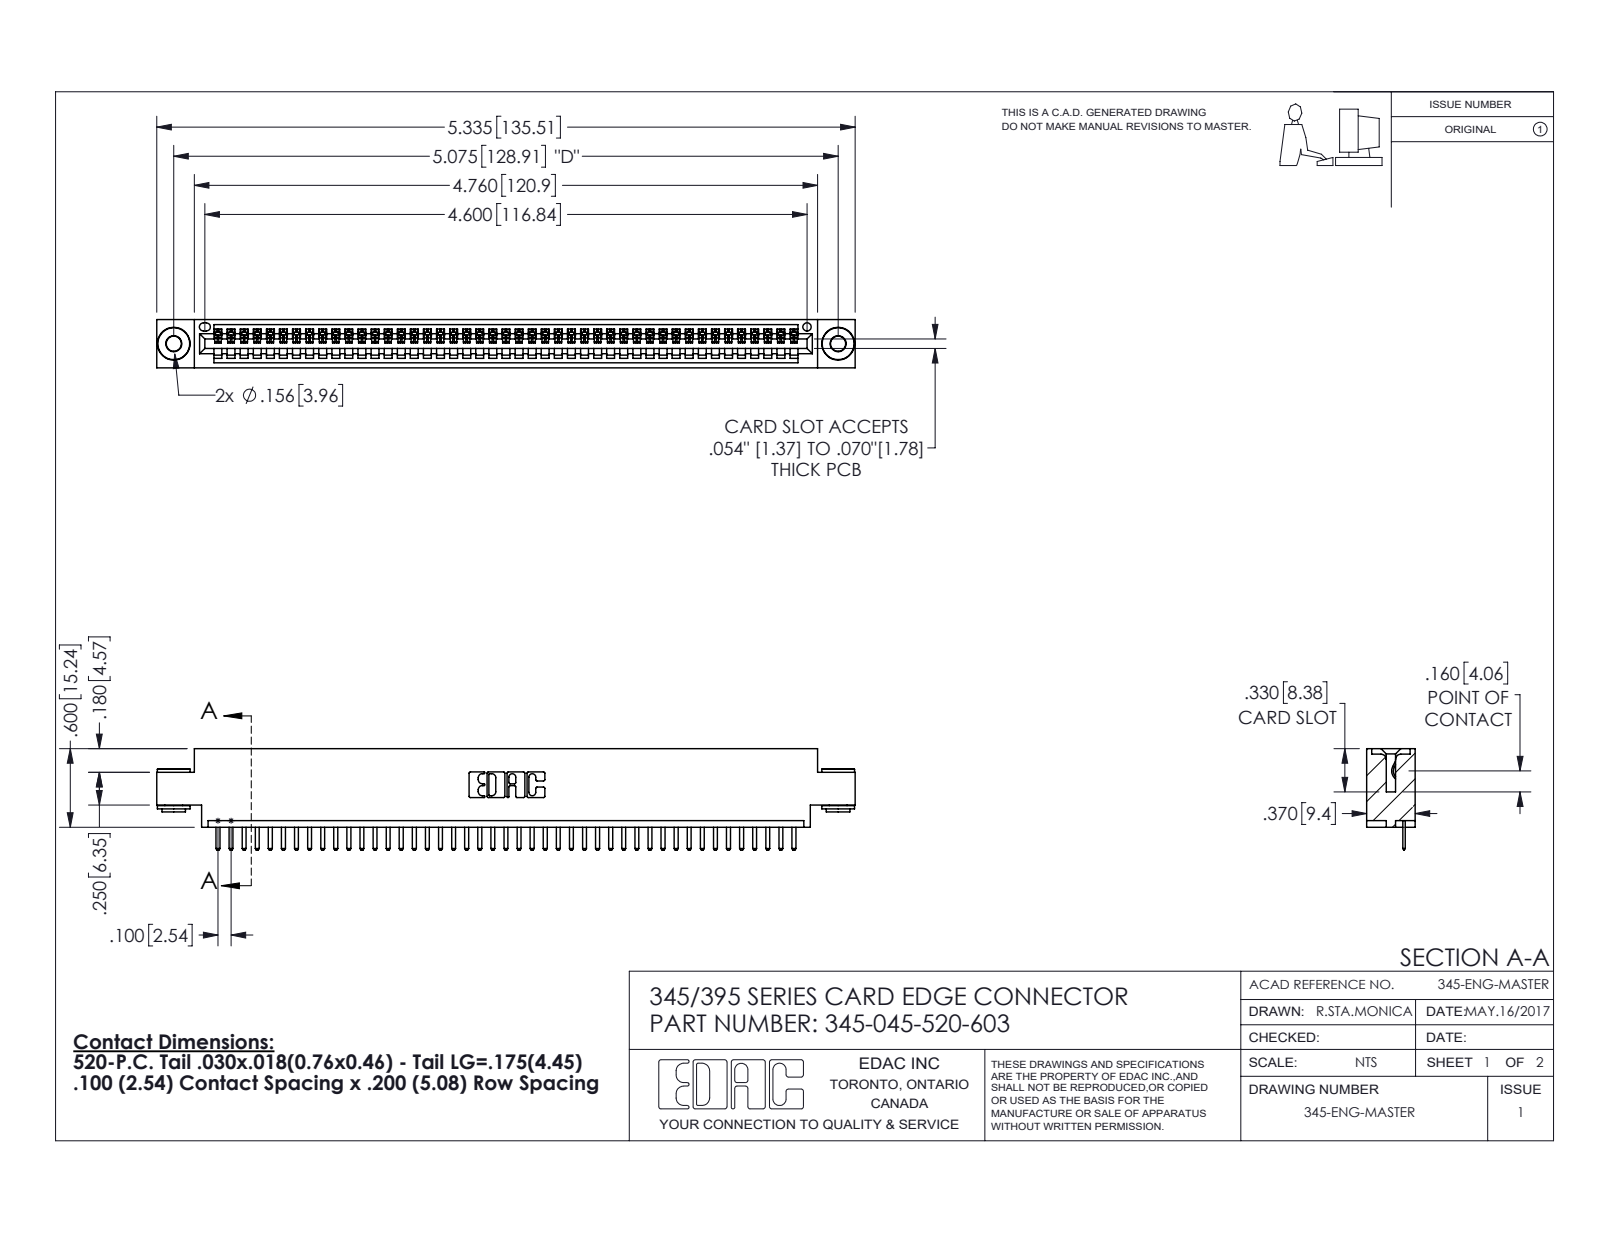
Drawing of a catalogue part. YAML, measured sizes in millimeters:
part_name: "345-292-001_345-293-120; 345 Part_0.170 Offset - 0.156 Dia-TH; 345-045-520-603; 345-250-002_345-250-002-102"
step_written_by: "SolidWorks 2016 (CONFIG_CONTROL_DESIGN)"
units: millimeters
bodies: {solids: 48, faces: 2958, planar: 1984, cylindrical: 966, other: 8}
overall_size: [135.5, 19.7, 9.4]
volume: 12700
surface_area: 16800
round_holes:
  - {diameter: 2.9, count: 2}
  - {diameter: 4, count: 2}
  - {diameter: 1.6, count: 1}
round_bosses_or_shafts:
  - {diameter: 6.4, count: 2}
  - {diameter: 4.6, count: 2}
  - {diameter: 3.5, count: 2}
partial_cylinders:
  - {radius: 0.3, count: 92}
  - {radius: 0.2, count: 90}
  - {radius: 0.3, count: 22}
  - {radius: 0.2, count: 6}
  - {radius: 0.8, count: 6}
  - {radius: 0.7, count: 3}
  - {radius: 0.8, count: 2}
  - {radius: 1, count: 2}
face_to_face_distances: [1.8, 7.6, 9.4, 5.1, 2.5, 6.9, 0.6, 5.7, 1.8, 4.4]
hole_center_spacings: [6.9, 122.9, 128.9]
